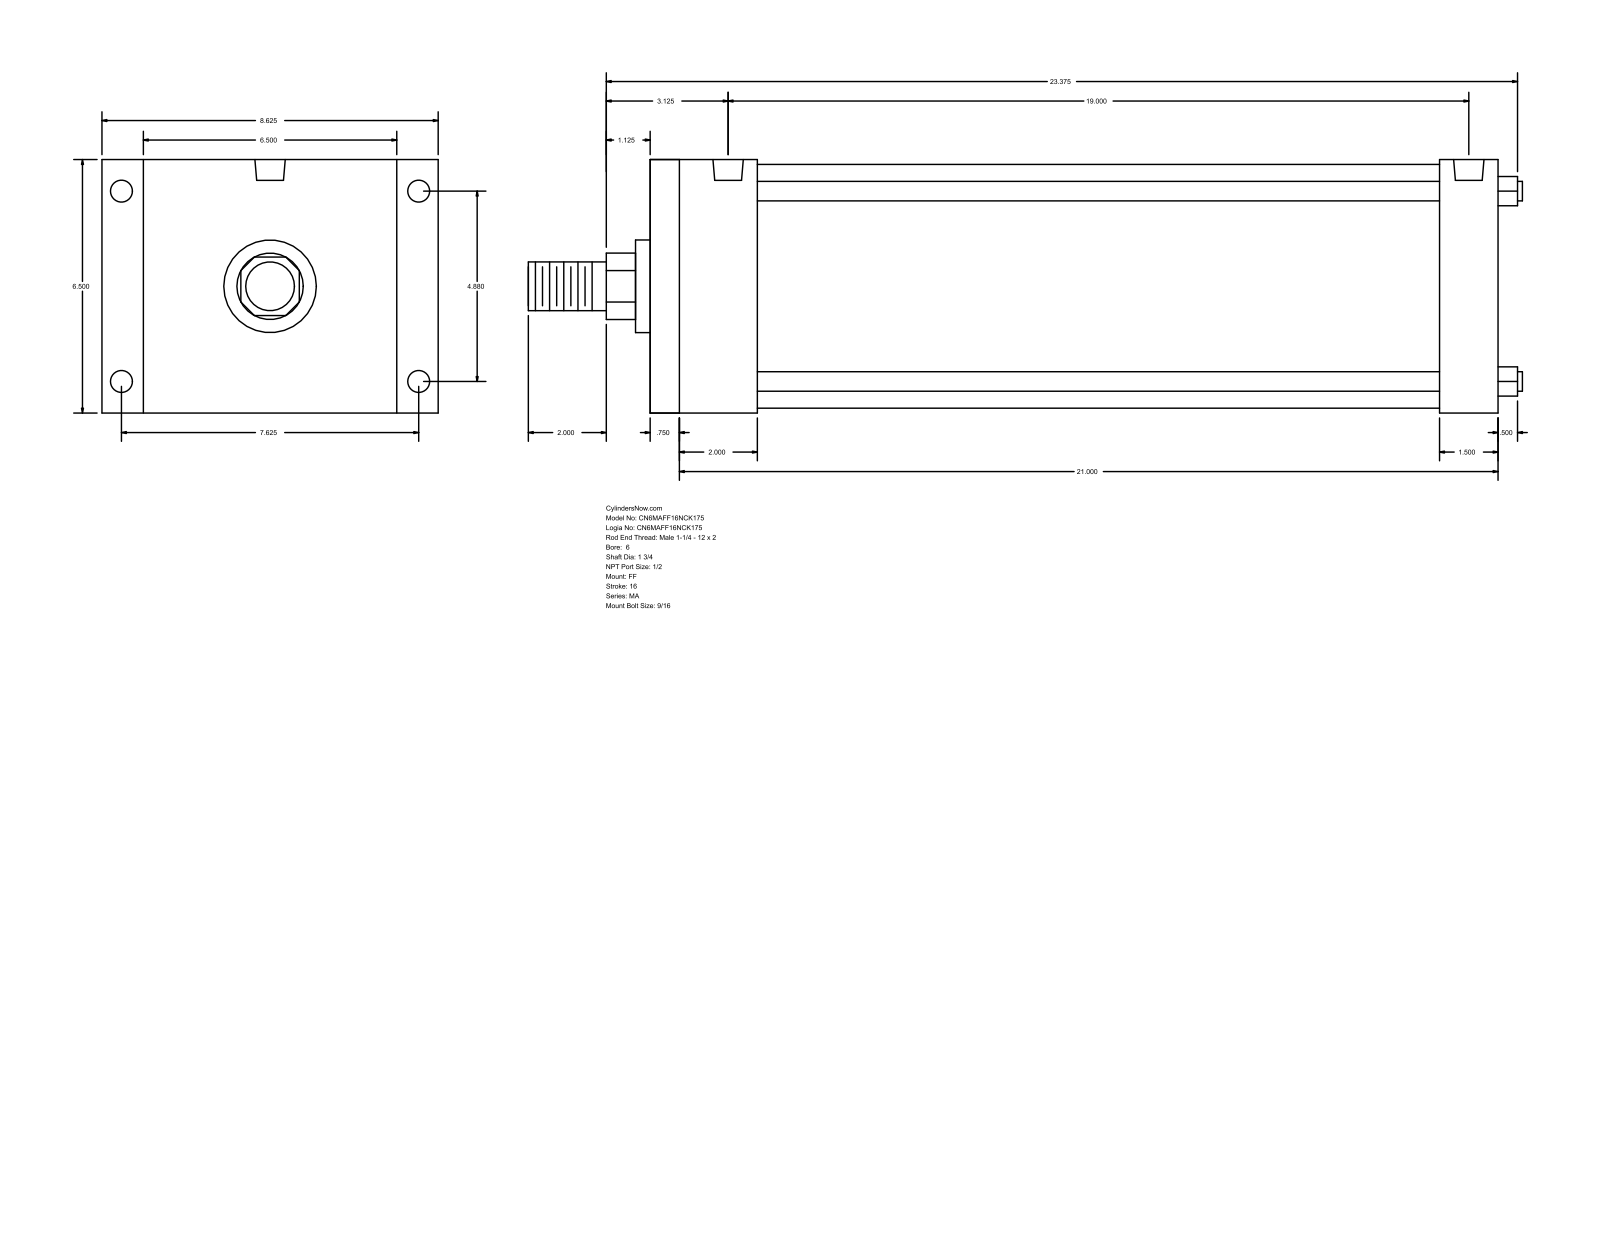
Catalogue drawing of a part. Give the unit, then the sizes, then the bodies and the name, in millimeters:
Units: millimetres
Overall size (bounding box): 647.7 × 219.07 × 165.1
Round holes (diameter × count): ⌀14.29 ×4, ⌀17.46 ×4, ⌀19.77 ×2
Round bosses / shafts (diameter × count): ⌀12.7 ×4, ⌀158.75 ×1, ⌀60.33 ×1, ⌀44.45 ×1, ⌀31.75 ×1
Partial cylindrical surfaces — rounded edges, fillets, slot ends (radius × count): R21.63 ×1
Main face-to-face distances: 165.1, 552.45, 19.05, 533.4, 69.85, 38.1, 50.8, 482.6, 514.35, 495.3
Hole centre spacings: 123.96, 193.68, 229.95, 482.6
Bodies: 0 solids, 92 faces (64 planar, 28 cylindrical, 0 other)
Part name (STEP PRODUCT): MA_FF__0600_1.75
STEP written by: GSSL Pune (CONFIG_CONTROL_DESIGN)
